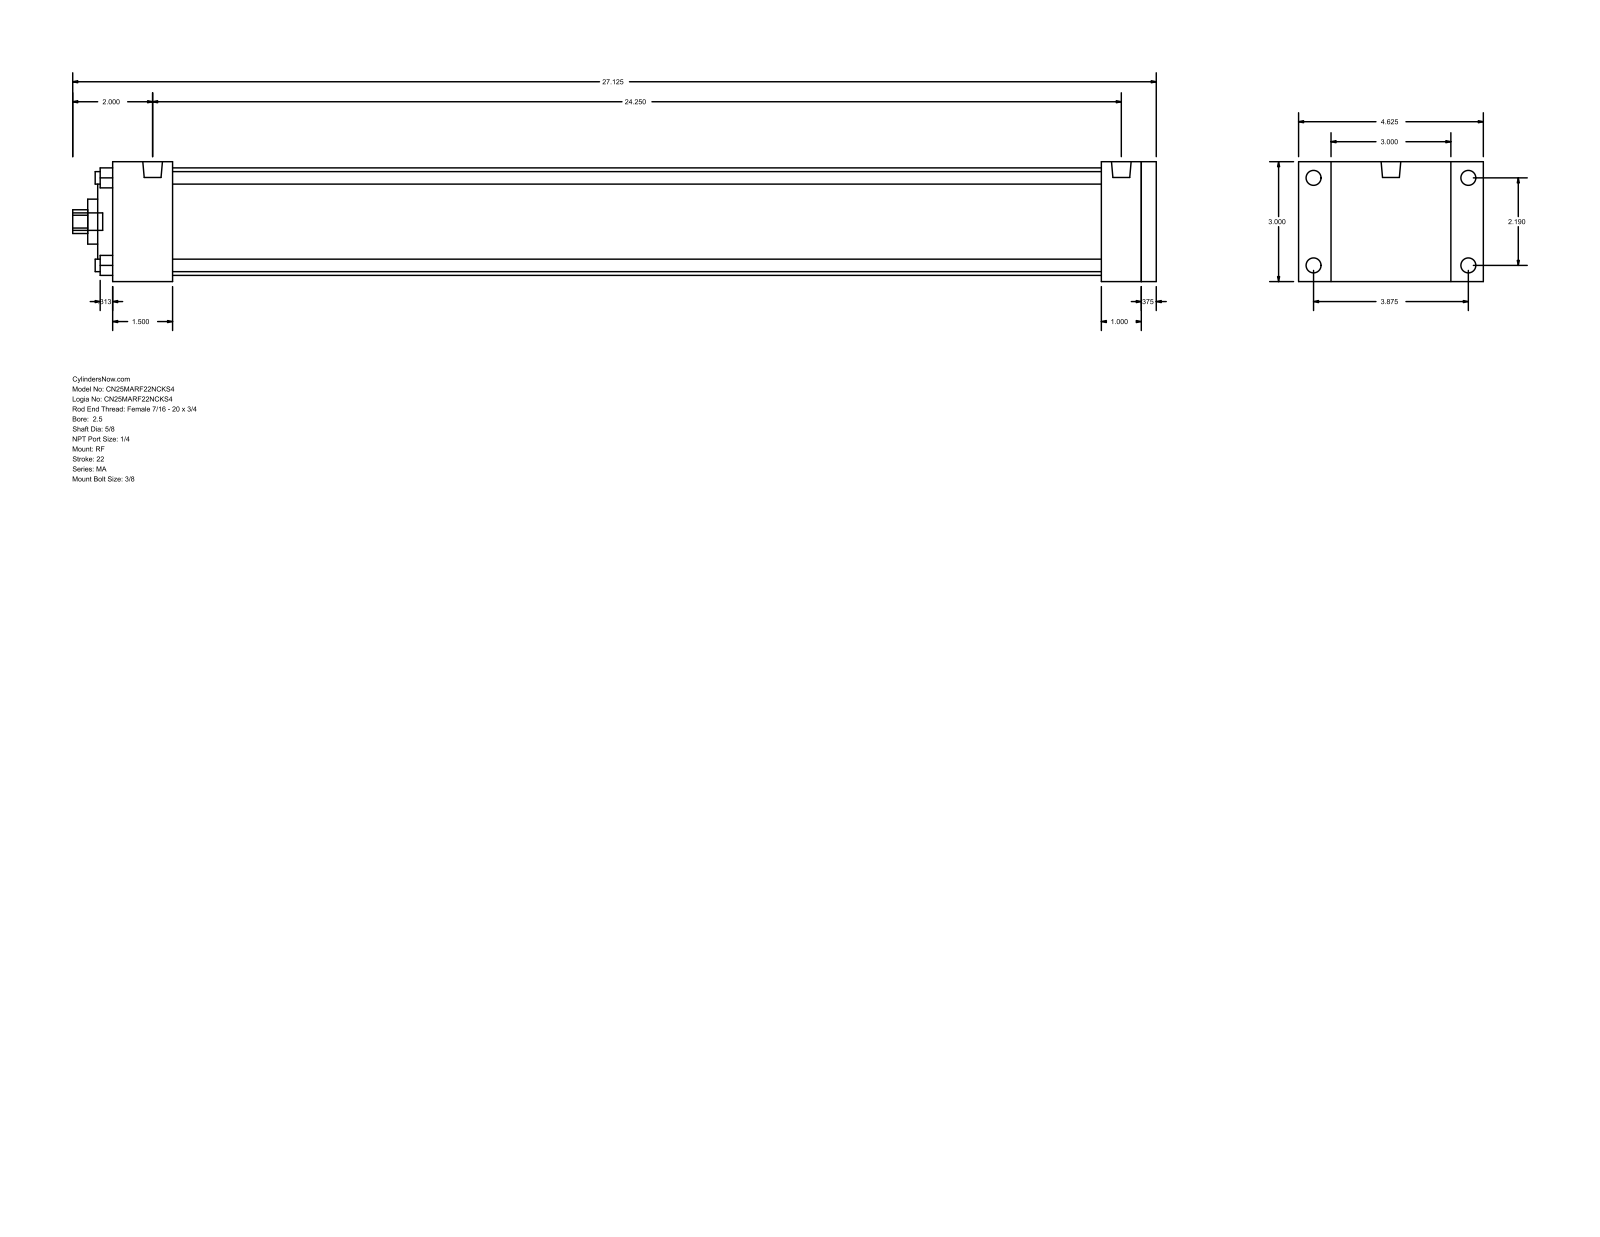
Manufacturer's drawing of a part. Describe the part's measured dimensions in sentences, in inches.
The part is named "MA_RF__0250_0.625". Its 3-D file was written by "GSSL Pune (CONFIG_CONTROL_DESIGN)". It is 0 solids with 94 faces: 65 planar, 29 cylindrical and 0 other. Overall it measures 27.125 by 4.625 by 3 inches. Round holes: 4 of diameter 0.313, 1 of diameter 0.625, 1 of diameter 1.125, 1 of diameter 2, 1 of diameter 2.69. Round bosses or shafts: 4 of diameter 0.375, 4 of diameter 0.313, 2 of diameter 0.492, 1 of diameter 0.437. Partial cylindrical surfaces (rounded edges, fillets, slot ends): 1 of radius 0.297. The main face-to-face distances are 3, 26.125, 0.375, 25.75, 1, 1.5, 24.75, 23.25, 24.25, 24.625. The hole center spacings are 1.548, 2.19, 3.097.
